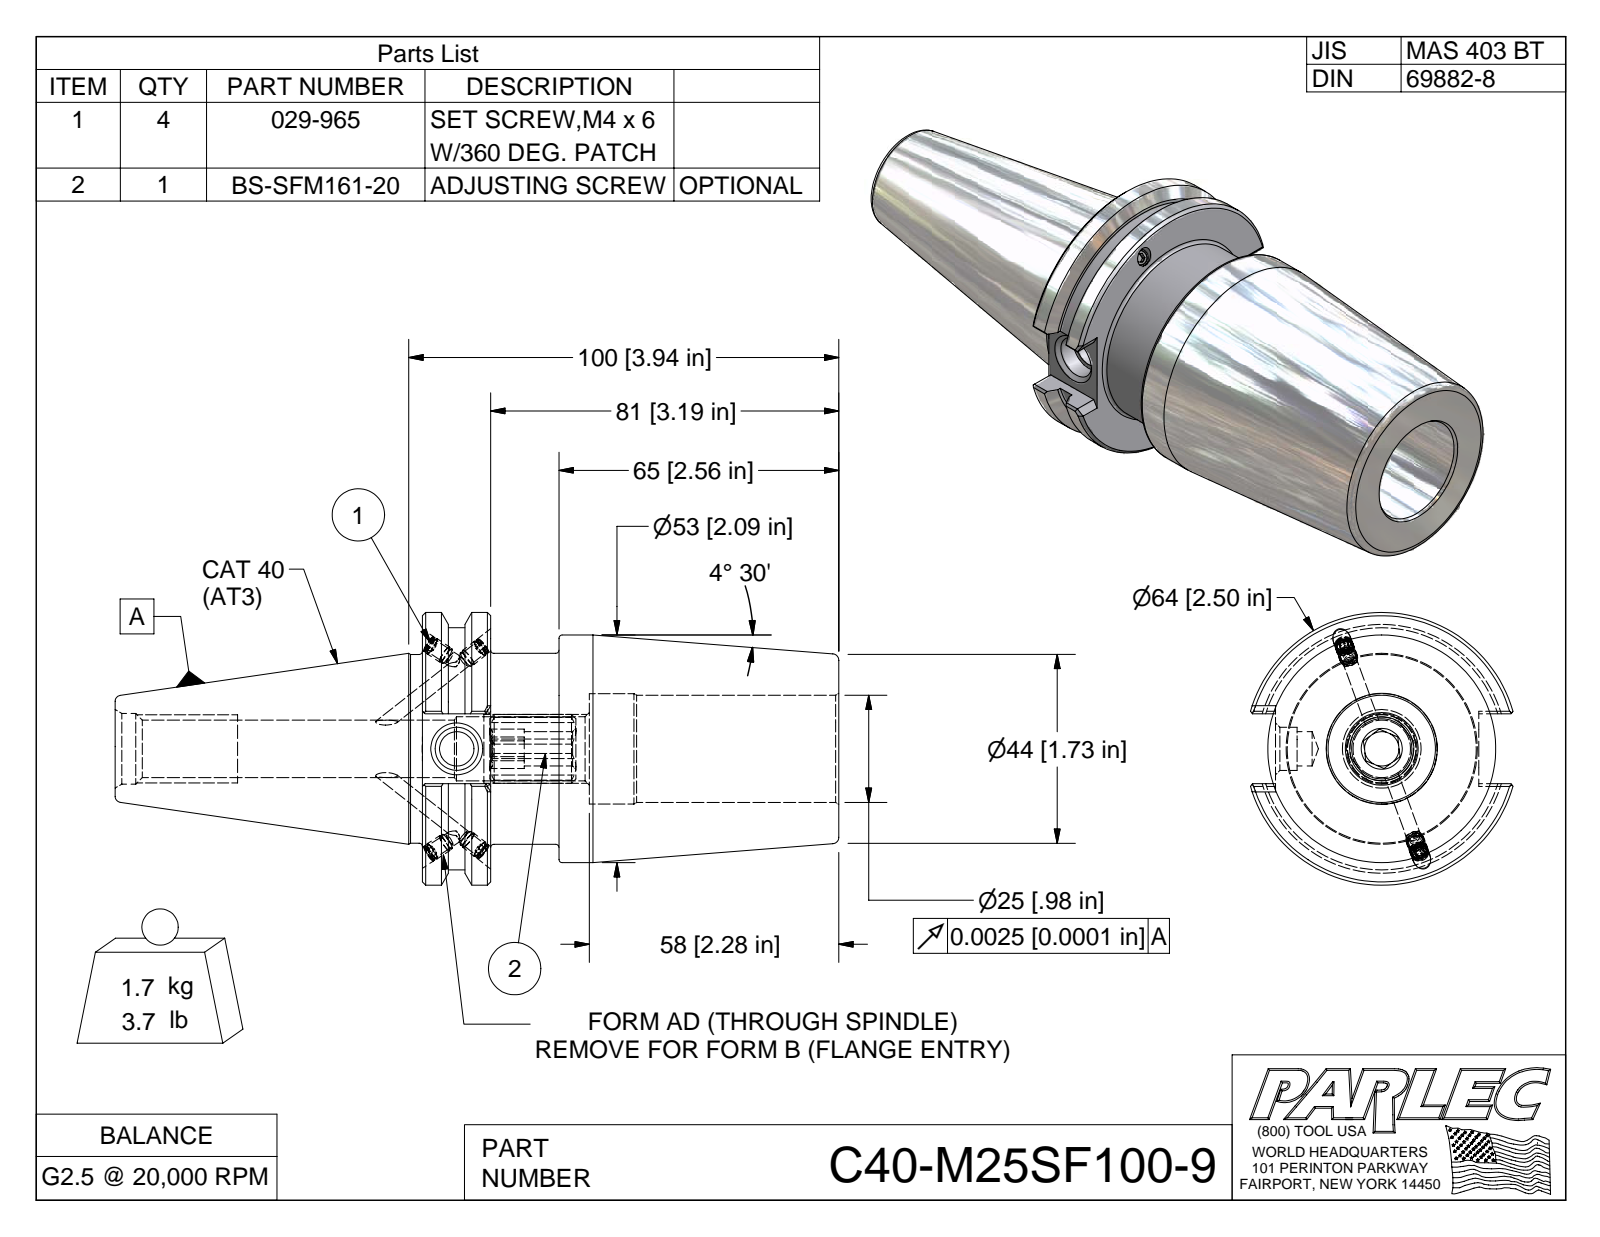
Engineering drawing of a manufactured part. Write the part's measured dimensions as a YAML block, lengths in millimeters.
part_name: "C40-M25SF100-9; C40BC-M25SF100-9-1; 029-965; BS-SFM161-20"
step_written_by: "Autodesk Inventor 2009 (AUTOMOTIVE_DESIGN)"
units: millimeters
bodies: {solids: 6, faces: 176, planar: 88, cylindrical: 33, other: 55}
overall_size: [168.3, 63.5, 61]
volume: 217500
surface_area: 41470
round_holes:
  - {diameter: 3.3, count: 4}
  - {diameter: 4.1, count: 4}
  - {diameter: 25, count: 1}
  - {diameter: 25.7, count: 1}
round_bosses_or_shafts:
  - {diameter: 4.2, count: 4}
  - {diameter: 4, count: 4}
  - {diameter: 63.5, count: 1}
  - {diameter: 56.4, count: 1}
  - {diameter: 53, count: 1}
  - {diameter: 44.5, count: 1}
  - {diameter: 43.9, count: 1}
partial_cylinders:
  - {radius: 8, count: 1}
face_to_face_distances: [15.9, 96.8, 80.9, 31.8, 65.1, 38.8, 23, 7.1, 58, 16.3]
